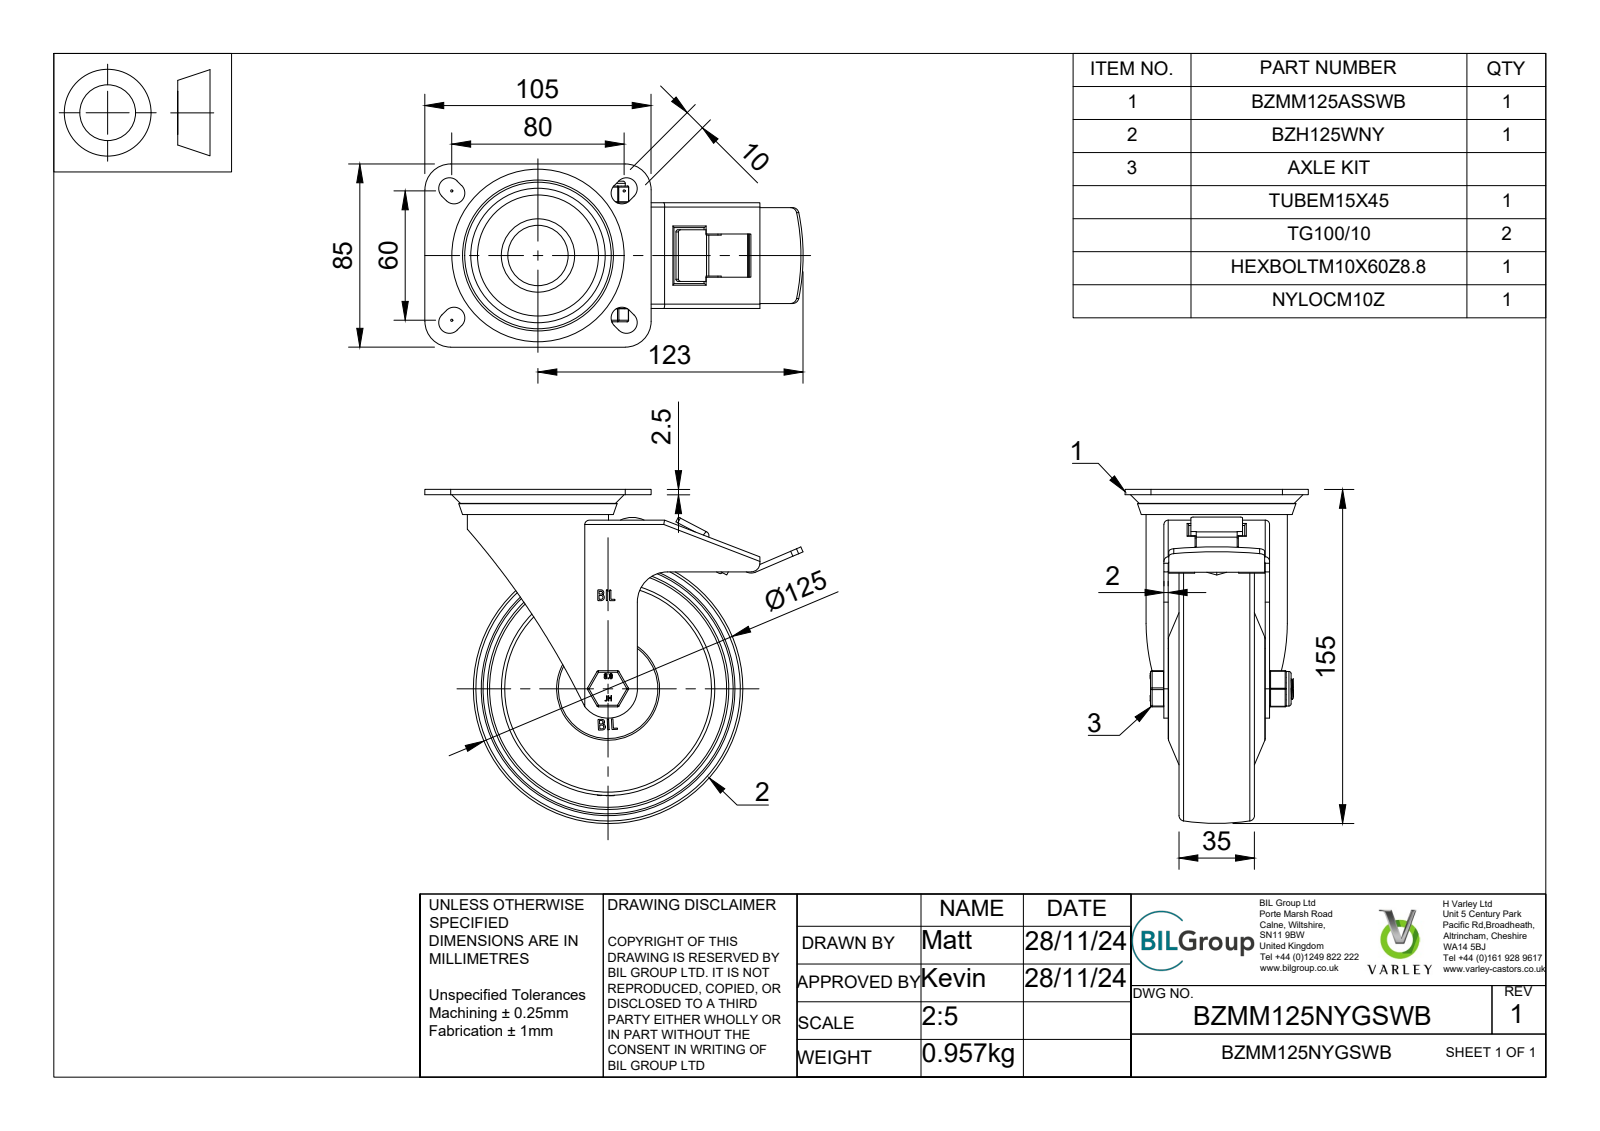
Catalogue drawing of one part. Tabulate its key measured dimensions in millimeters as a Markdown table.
| quantity | value |
| --- | --- |
| part name | BZMM125NYGSWB v3; BZMM125ASSWB v1; ZINC PLATED, PRESSED STEEL TOP PLATE; ZINC PLATED, PRESSED STEEL FORKS (+8 more) |
| STEP written by | Autodesk Translation Framework v13.20.0.188 (AP242_MANAGED_MODEL_BASED_3D_ENGINEERING_MIM_LF) |
| units | millimeters |
| bodies | 15 solids, 963 faces (445 planar, 205 cylindrical, 313 other) |
| overall size | 175.5 × 155 × 85 |
| volume | 273 219 mm³ |
| surface area | 172 857 mm² |
| round holes (diameter × count) | 6 × 2, 10 × 1, 10.2 × 1, 10.5 × 1, 12 × 1, 15.2 × 1, 28 × 1, 40 × 1, 61.5 × 1, 98 × 1, 112 × 1 |
| round bosses / shafts (diameter × count) | 99 × 1, 65.5 × 1, 34 × 1, 16 × 1, 15.5 × 1, 14.95 × 1, 9.85 × 1, 8.14 × 1 |
| partial cylindrical surfaces (radius × count) | 0.5 × 18, 0.75 × 16, 1.5 × 12, 5 × 9, 1 × 8, 2 × 6, 3 × 4, 12 × 4 |
| main face-to-face distances | 2, 19.25, 25.75, 2.5, 0.5, 21.25, 27.75, 47, 5, 6.5 |
| hole center spacings | 43.75 |
